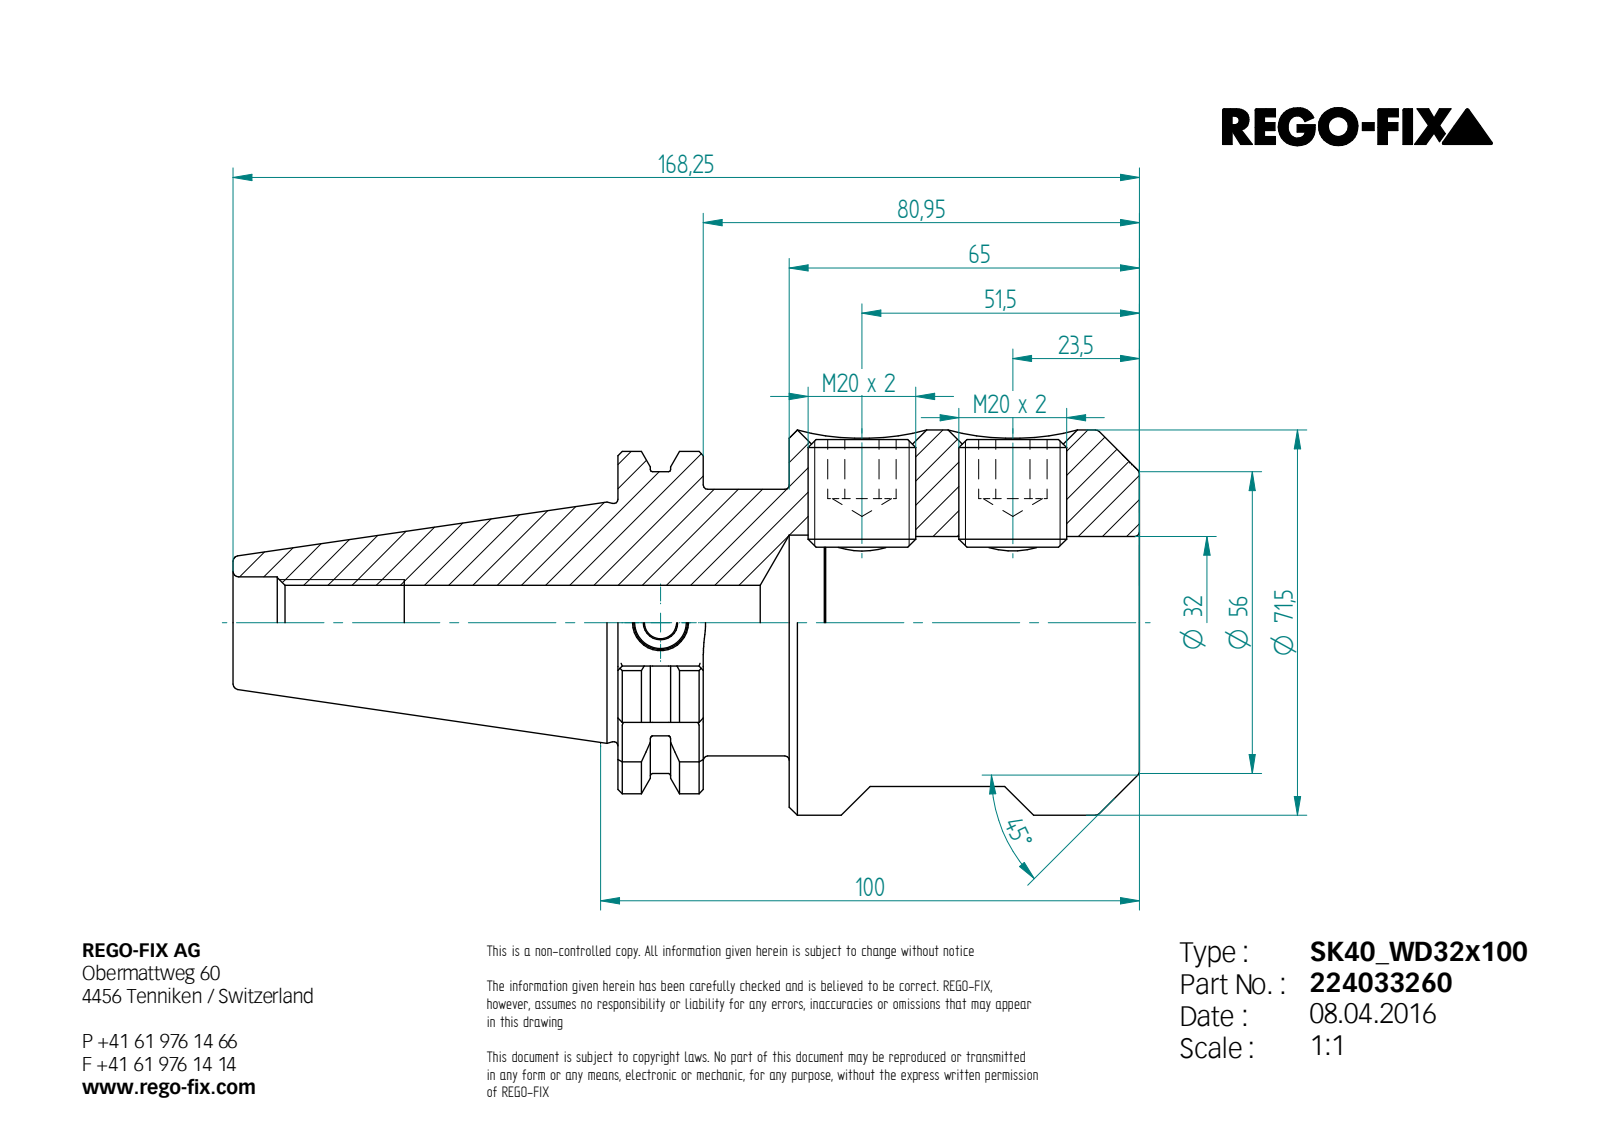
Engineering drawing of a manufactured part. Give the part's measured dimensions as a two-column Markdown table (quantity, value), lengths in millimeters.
| quantity | value |
| --- | --- |
| STEP written by | Unknown (AUTOMOTIVE_DESIGN) |
| units | millimeters |
| bodies | 3 solids, 153 faces (73 planar, 34 cylindrical, 46 other) |
| overall size | 168.25 × 71.5 × 71.5 |
| volume | 323 081 mm³ |
| surface area | 52 838 mm² |
| round holes (diameter × count) | 17.84 × 2, 6 × 1, 10 × 1, 13.84 × 1, 17 × 1, 32 × 1, 32.5 × 1 |
| round bosses / shafts (diameter × count) | 20 × 2, 71.5 × 1, 49.5 × 1 |
| partial cylindrical surfaces (radius × count) | 0.5 × 11, 8.05 × 1, 28 × 1, 31.77 × 1 |
| main face-to-face distances | 65, 31.8, 96.8, 15.85, 15.95, 80.95, 44.4, 11, 24.25, 64.4 |
| hole center spacings | 28 |
